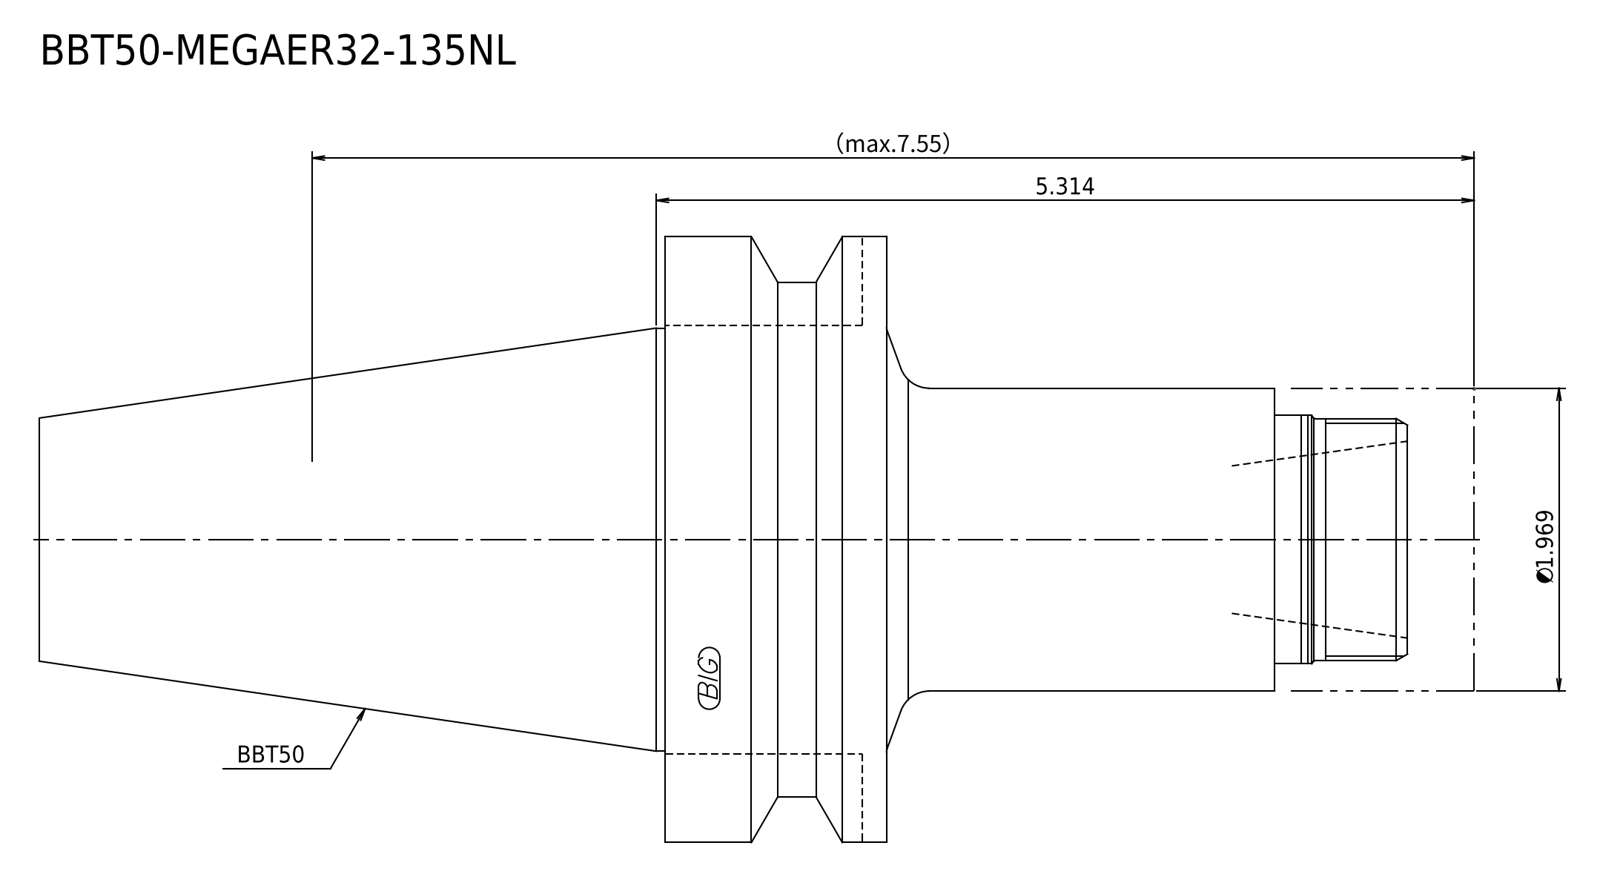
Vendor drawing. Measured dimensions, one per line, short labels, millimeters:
written by: Kubotek KeyCreator 2011 V10.0.2 (22737) (automotive_design)
unit: mm
bodies: 2 solids, 21 faces (7 planar, 8 cylindrical, 6 other)
size: 6014.7 × 2540 × 2540
volume: 12 060 000 000 mm³; area: 42 200 000 mm²
bosses: 1× ⌀2540, 1× ⌀2159, 1× ⌀1774.2, 1× ⌀1270, 1× ⌀1041.4, 1× ⌀1016
face distances: 927.1, 2623.8, 767.1, 2463.8, 3390.9, 1696.7, 6014.7, 5247.6, 3550.9, 279.4
